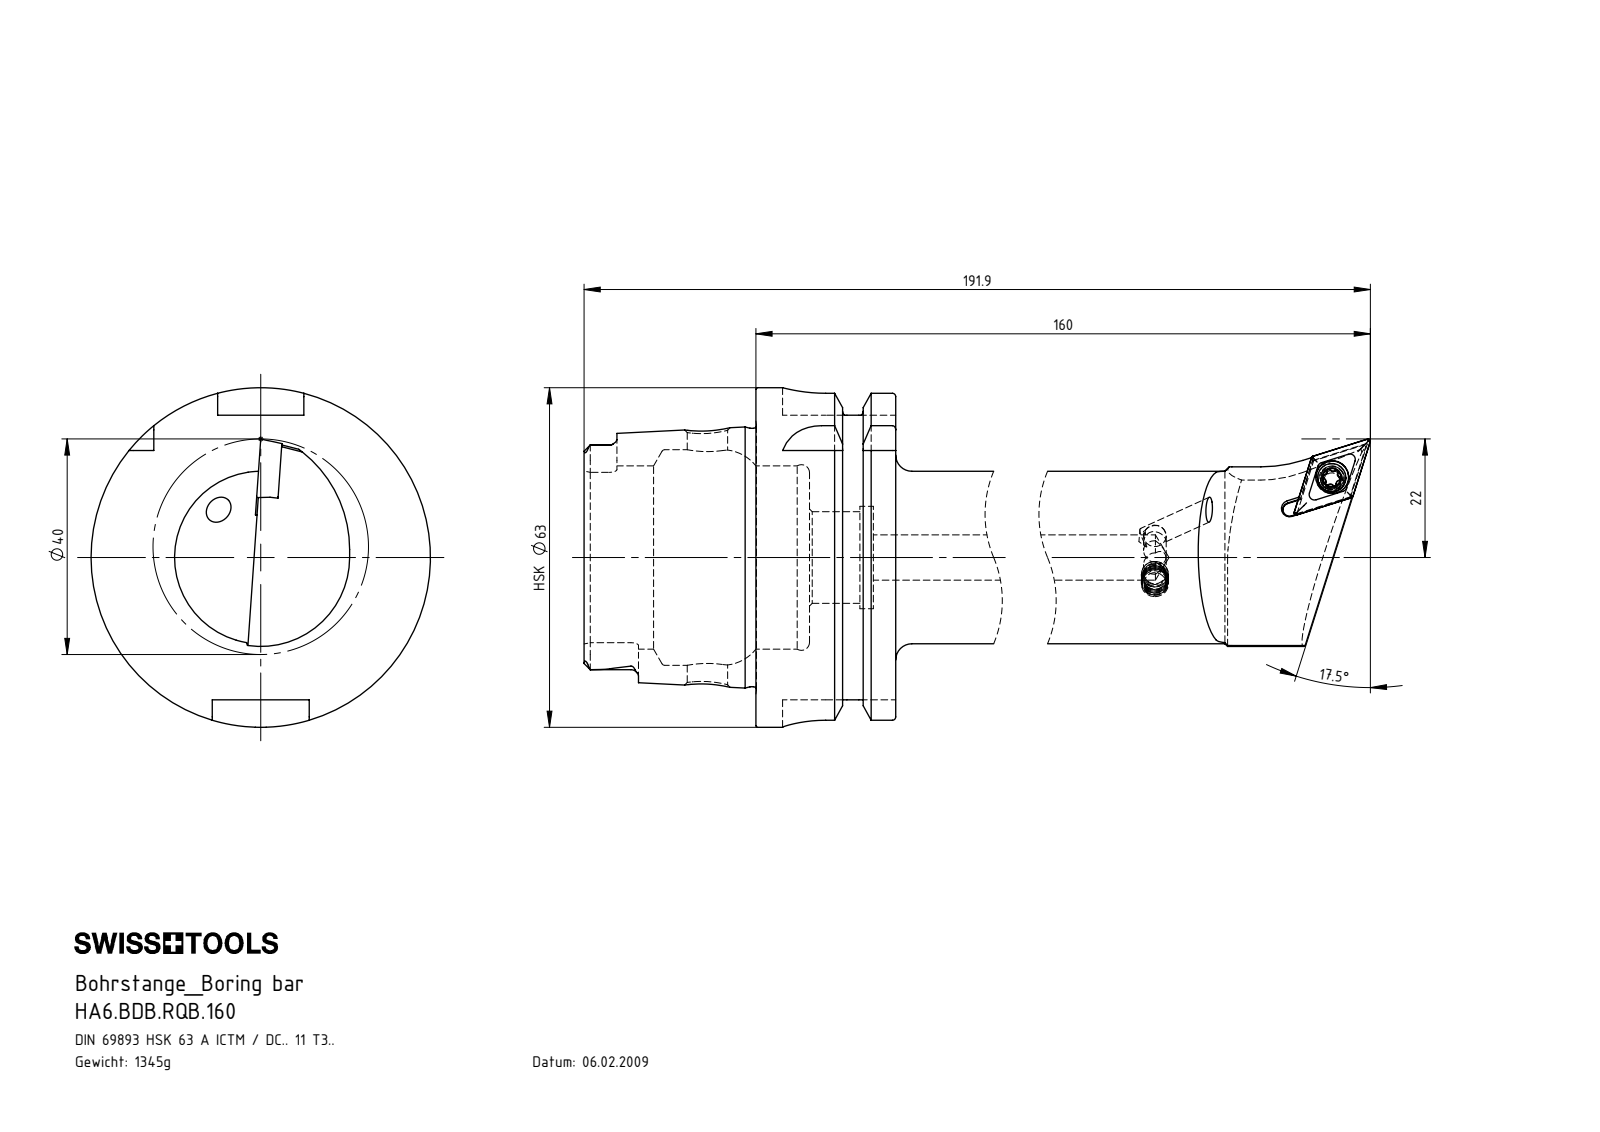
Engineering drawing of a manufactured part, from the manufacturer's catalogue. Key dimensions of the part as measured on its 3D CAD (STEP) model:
Part name (STEP PRODUCT): HA6.BDB.RQB.160; DCMT11T304; WCB-ER2.001.009_A; HA6-BDB.RQB.160_B (+1 more)
STEP written by: SolidWorks 2017 (AUTOMOTIVE_DESIGN)
Units: millimetres
Bodies: 5 solids, 231 faces (78 planar, 59 cylindrical, 94 other)
Overall size (bounding box): 191.9 × 63 × 63
Volume: 170 867 mm³ · Surface area: 38 353 mm²
Round holes (diameter × count): ⌀4.2 ×2, ⌀3.3 ×1, ⌀4 ×1, ⌀4.4 ×1, ⌀6.1 ×1, ⌀7.5 ×1, ⌀8.4 ×1, ⌀17 ×1, ⌀19 ×1, ⌀34 ×1, ⌀40 ×1
Round bosses / shafts (diameter × count): ⌀63 ×1, ⌀54.95 ×1, ⌀47.94 ×1, ⌀32 ×1, ⌀5.25 ×1, ⌀5 ×1, ⌀4 ×1
Partial cylindrical surfaces — rounded edges, fillets, slot ends (radius × count): R0.34 ×6, R0.59 ×6, R1.4 ×6, R8 ×4, R2.82 ×2, R2.88 ×2, R1.25 ×1, R3 ×1
Main face-to-face distances: 25.95, 16, 9.95, 31.9, 41.85, 57.85, 52.8, 21.8, 11.85, 53.7
